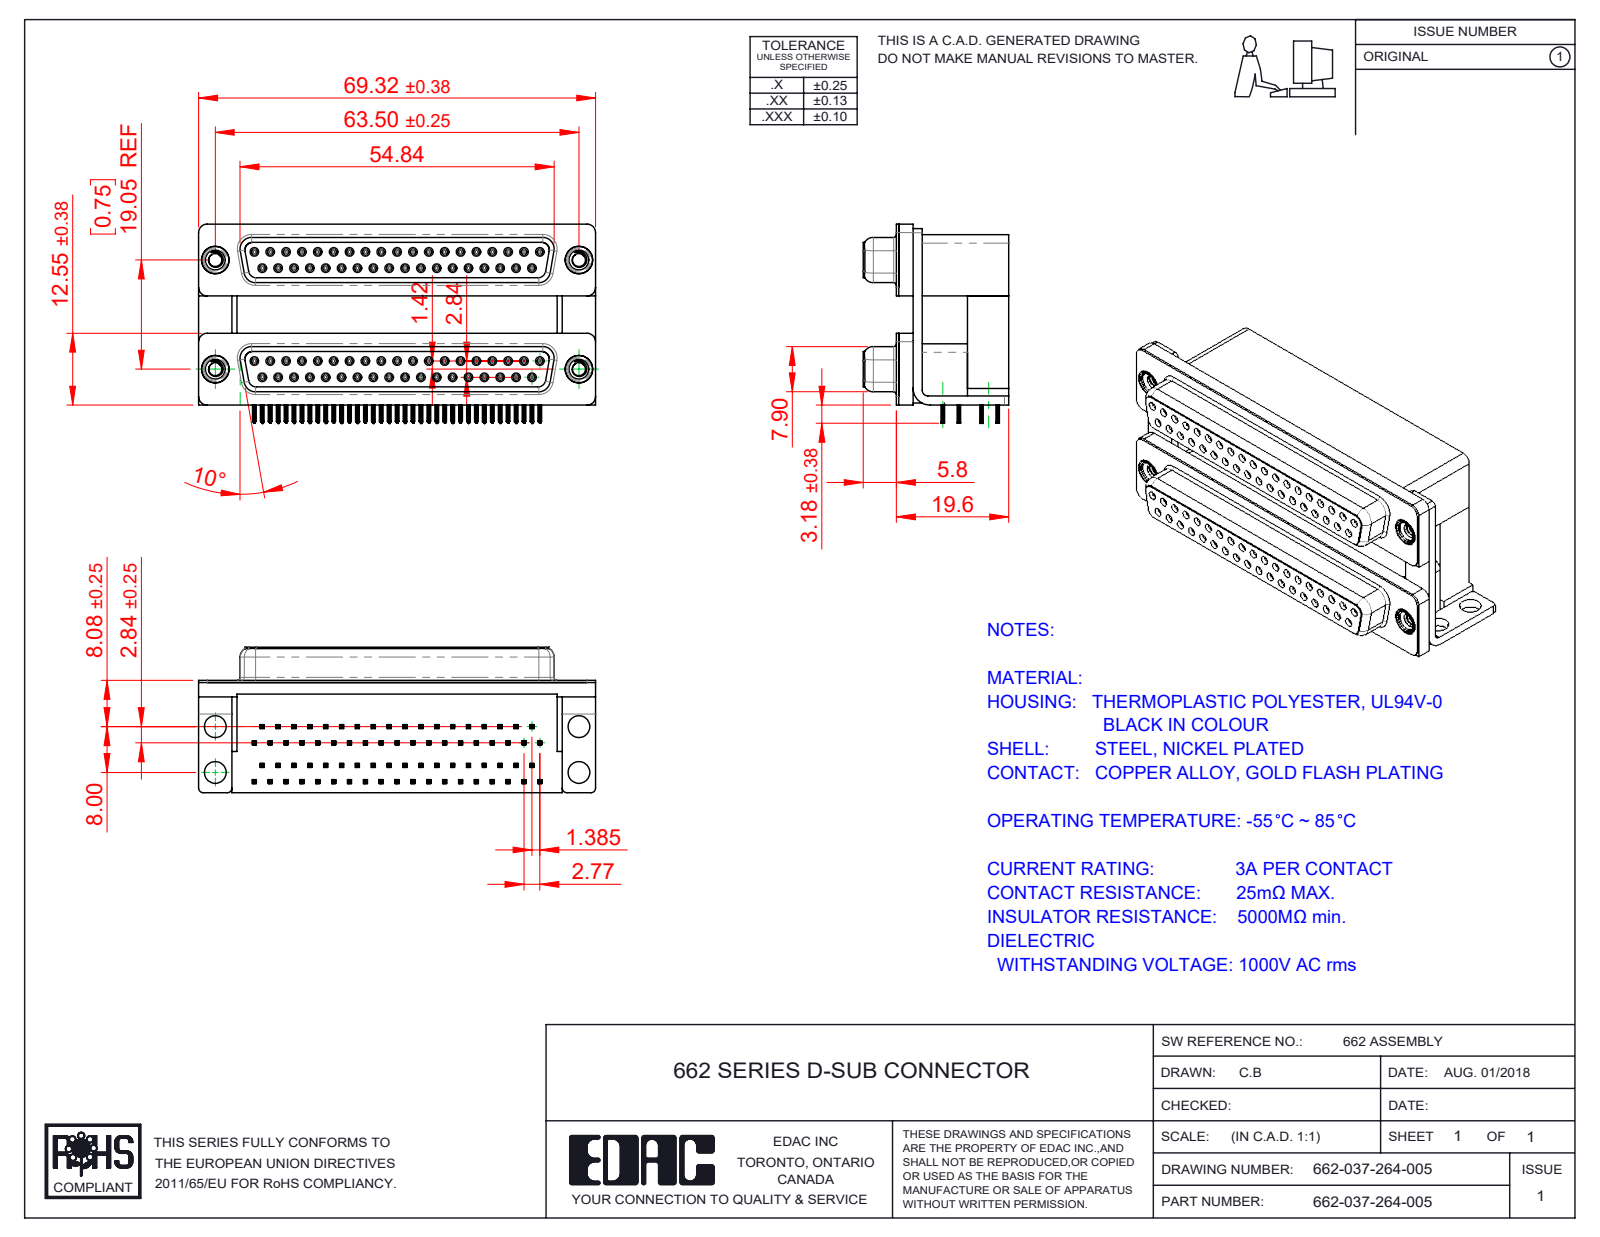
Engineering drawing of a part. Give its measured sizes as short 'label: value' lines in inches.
name: 662-037-264-005; 662 Contact Top Upper_M; 662 Contact Bottom Upper_M; 662 Shell_37 Contacts (+7 more)
written by: SolidWorks 2020 (CONFIG_CONTROL_DESIGN)
unit: in
bodies: 85 solids, 11308 faces (5232 planar, 2560 cylindrical, 3516 other)
size: 2.729 × 1.369 × 1
volume: 2.018 in³; area: 54.61 in²
holes: 74× ⌀0.031, 74× ⌀0.035, 4× ⌀0.089, 4× ⌀0.138, 4× ⌀0.15, 4× ⌀0.157, 4× ⌀0.189, 4× ⌀0.197
bosses: 74× ⌀0.047, 4× ⌀0.193, 4× ⌀0.187, 4× ⌀0.154
rounds: 592× R0.004, 296× R0.006, 148× R0.014, 74× R0.013, 36× R0.011, 16× R0.053, 12× R0.059, 8× R0.02
face distances: 0.75, 0.472, 0.756, 0.016, 0.283, 0.244, 0.421, 0.112, 0.736, 0.488
hole spacings: 0.124, 0.109, 0.218, 0.327, 0.436, 0.872, 0.545, 0.763
